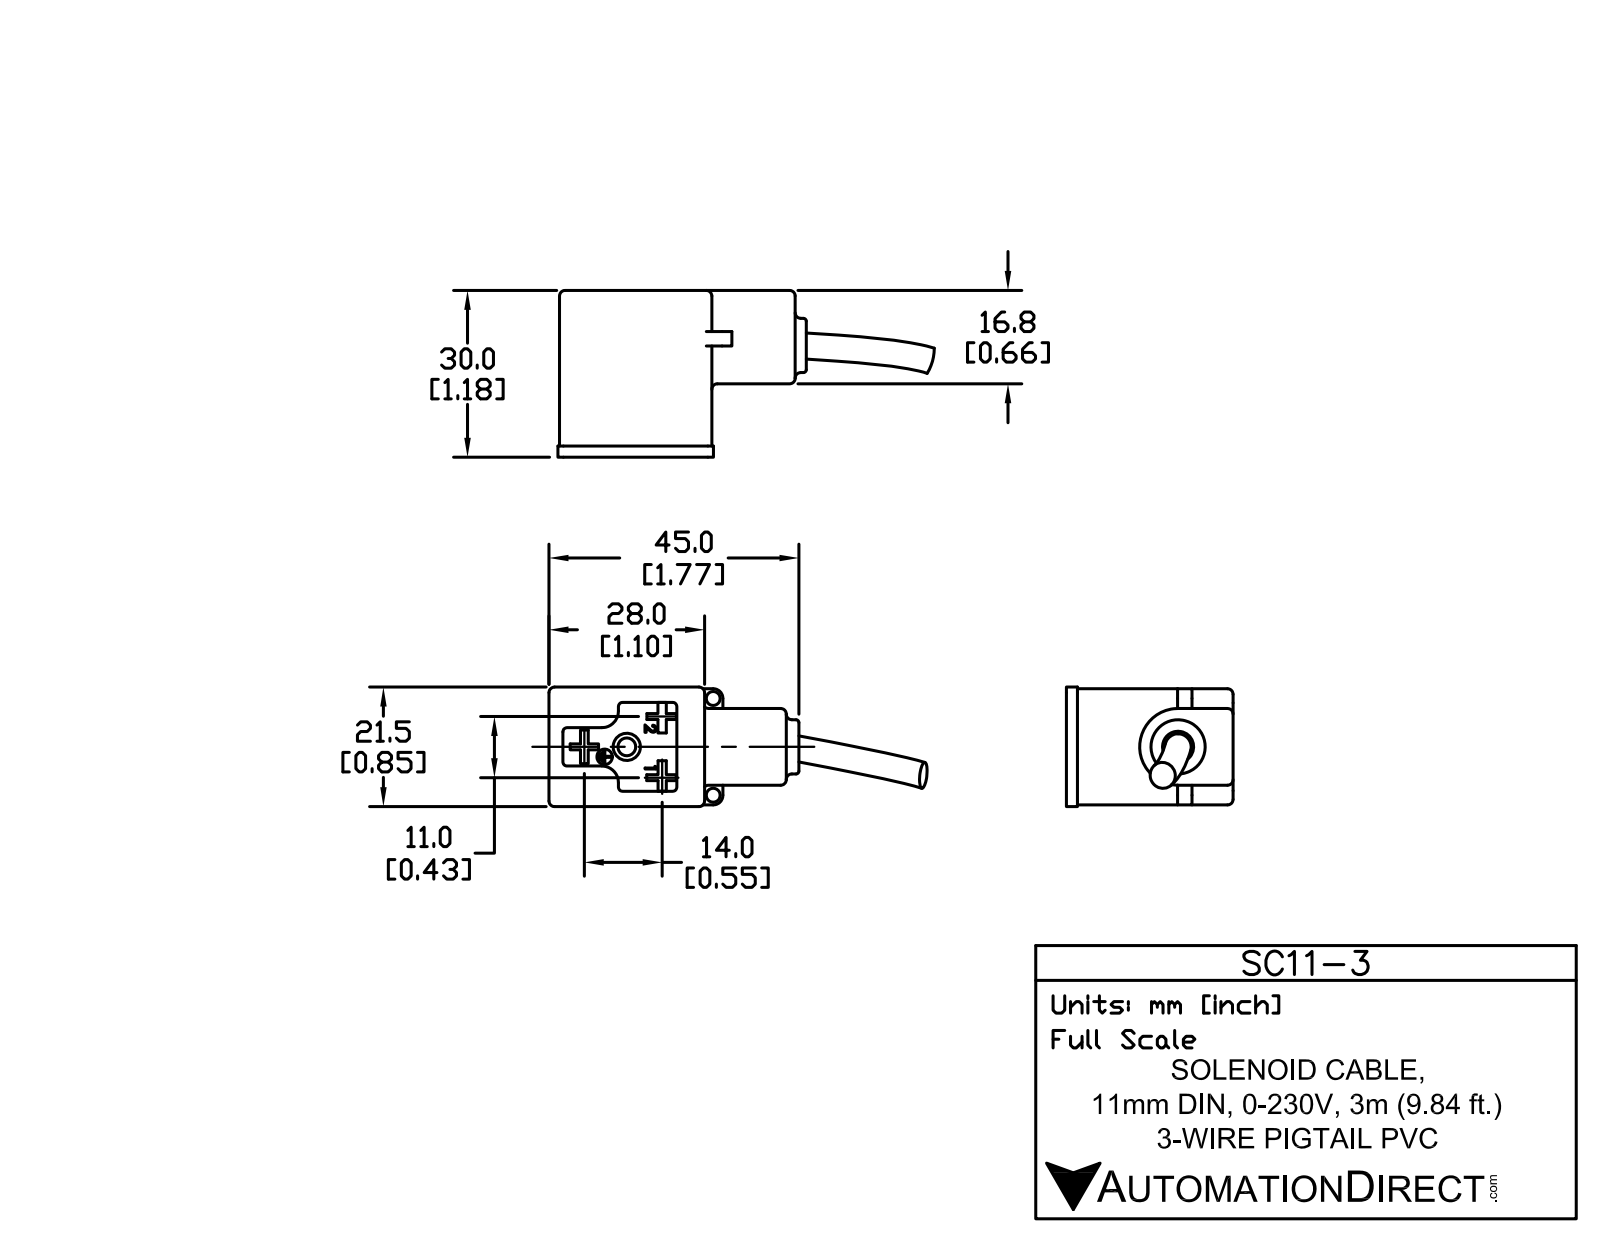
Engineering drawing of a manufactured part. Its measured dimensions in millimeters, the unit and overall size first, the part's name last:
Units: millimetres
Overall size (bounding box): 67.77 × 34.3 × 21.5
Round holes (diameter × count): ⌀2.5 ×2, ⌀2.78 ×1, ⌀3.2 ×1, ⌀4.9 ×1, ⌀5.6 ×1, ⌀6.6 ×1
Round bosses / shafts (diameter × count): ⌀9.75 ×1, ⌀6.5 ×1, ⌀2.75 ×1
Partial cylindrical surfaces — rounded edges, fillets, slot ends (radius × count): R0.75 ×21, R1 ×6, R1.75 ×2, R3 ×2, R6.9 ×1
Main face-to-face distances: 20.9, 2, 28, 30, 27.4, 3.55, 17.35, 7, 9.45, 27.95
Hole centre spacings: 17.82, 21.65, 4.27, 17.4
Volume: 19 925 mm³ · Surface area: 7 593 mm²
Bodies: 3 solids, 197 faces (131 planar, 45 cylindrical, 21 other)
Part name (STEP PRODUCT): SC11-3
STEP written by: SolidWorks 2011 (AUTOMOTIVE_DESIGN)
